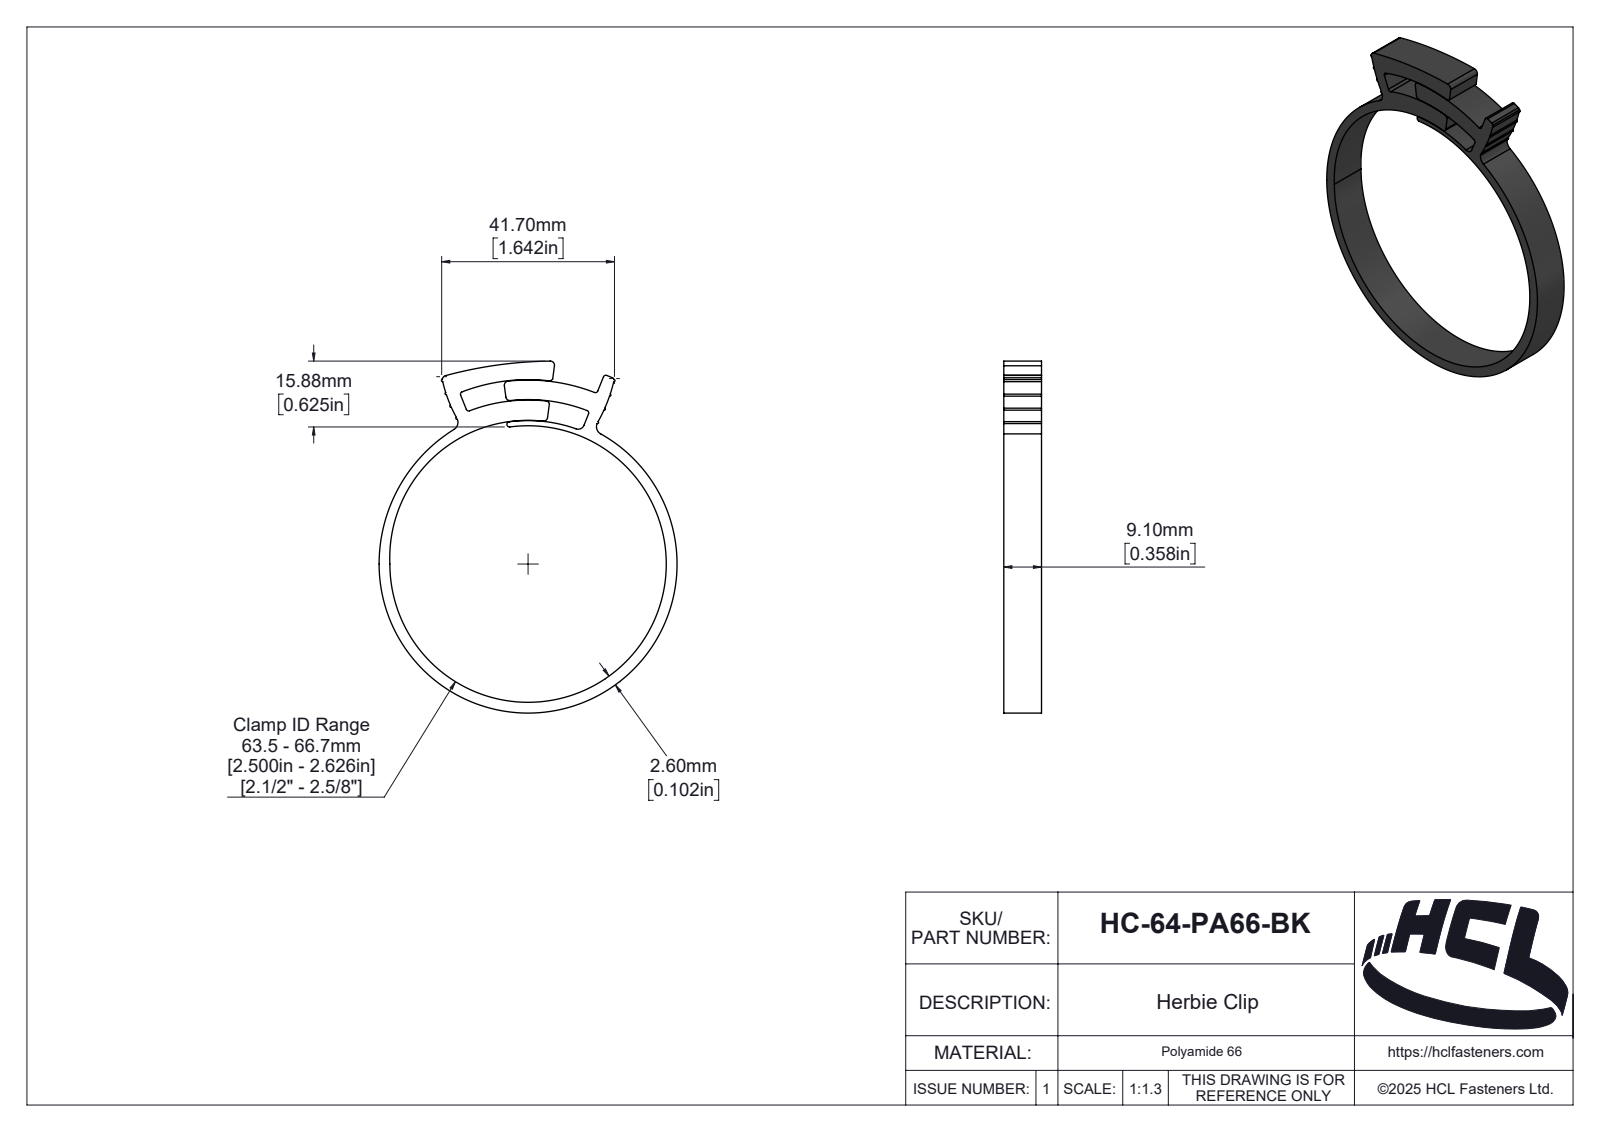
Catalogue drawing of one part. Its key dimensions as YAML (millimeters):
part_name: "HC-64-PA66-BK"
step_written_by: "SolidWorks 2025 (AUTOMOTIVE_DESIGN)"
units: millimeters
bodies: {solids: 1, faces: 161, planar: 13, cylindrical: 99, other: 49}
overall_size: [84.89, 71.9, 9.1]
volume: 8084
surface_area: 7254
partial_cylinders:
  - {radius: 0.25, count: 8}
  - {radius: 0.6, count: 6}
  - {radius: 1, count: 5}
  - {radius: 2, count: 2}
  - {radius: 0.17, count: 1}
  - {radius: 0.62, count: 1}
  - {radius: 0.67, count: 1}
  - {radius: 0.84, count: 1}
face_to_face_distances: [9.1]
